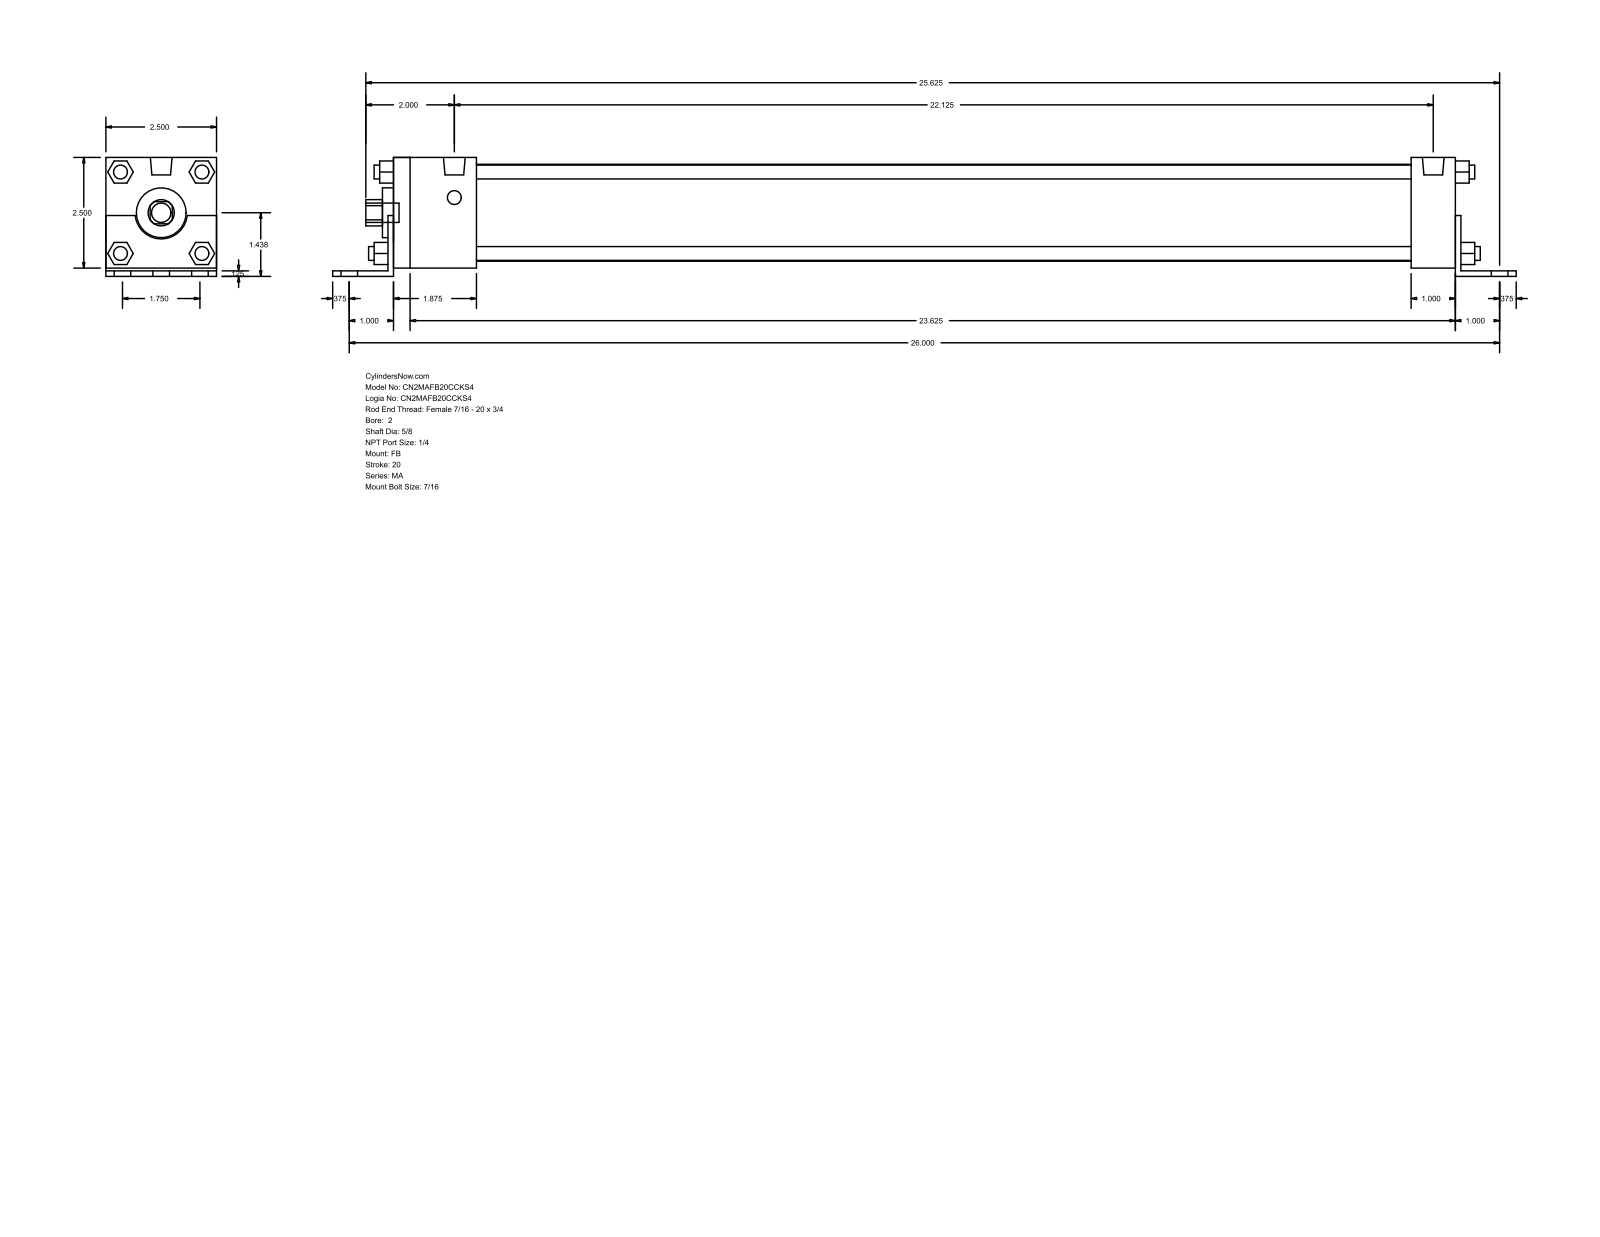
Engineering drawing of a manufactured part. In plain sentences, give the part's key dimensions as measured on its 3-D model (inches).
The part is named "MA_FB__0200_0.625". Its 3-D file was written by "GSSL Pune (CONFIG_CONTROL_DESIGN)". It is 0 solids with 140 faces: 105 planar, 35 cylindrical and 0 other. Overall it measures 26.75 by 2.687 by 2.5 inches. Round holes: 1 of diameter 0.625, 1 of diameter 1.125, 1 of diameter 2.19. Round bosses or shafts: 8 of diameter 0.313, 7 of diameter 0.437, 2 of diameter 0.492. Partial cylindrical surfaces (rounded edges, fillets, slot ends): 1 of radius 0.297, 1 of radius 0.593. The main face-to-face distances are 2.5, 0.125, 0.187, 2.687, 0.063, 2.563, 24, 24.25, 0.125, 24.125.
